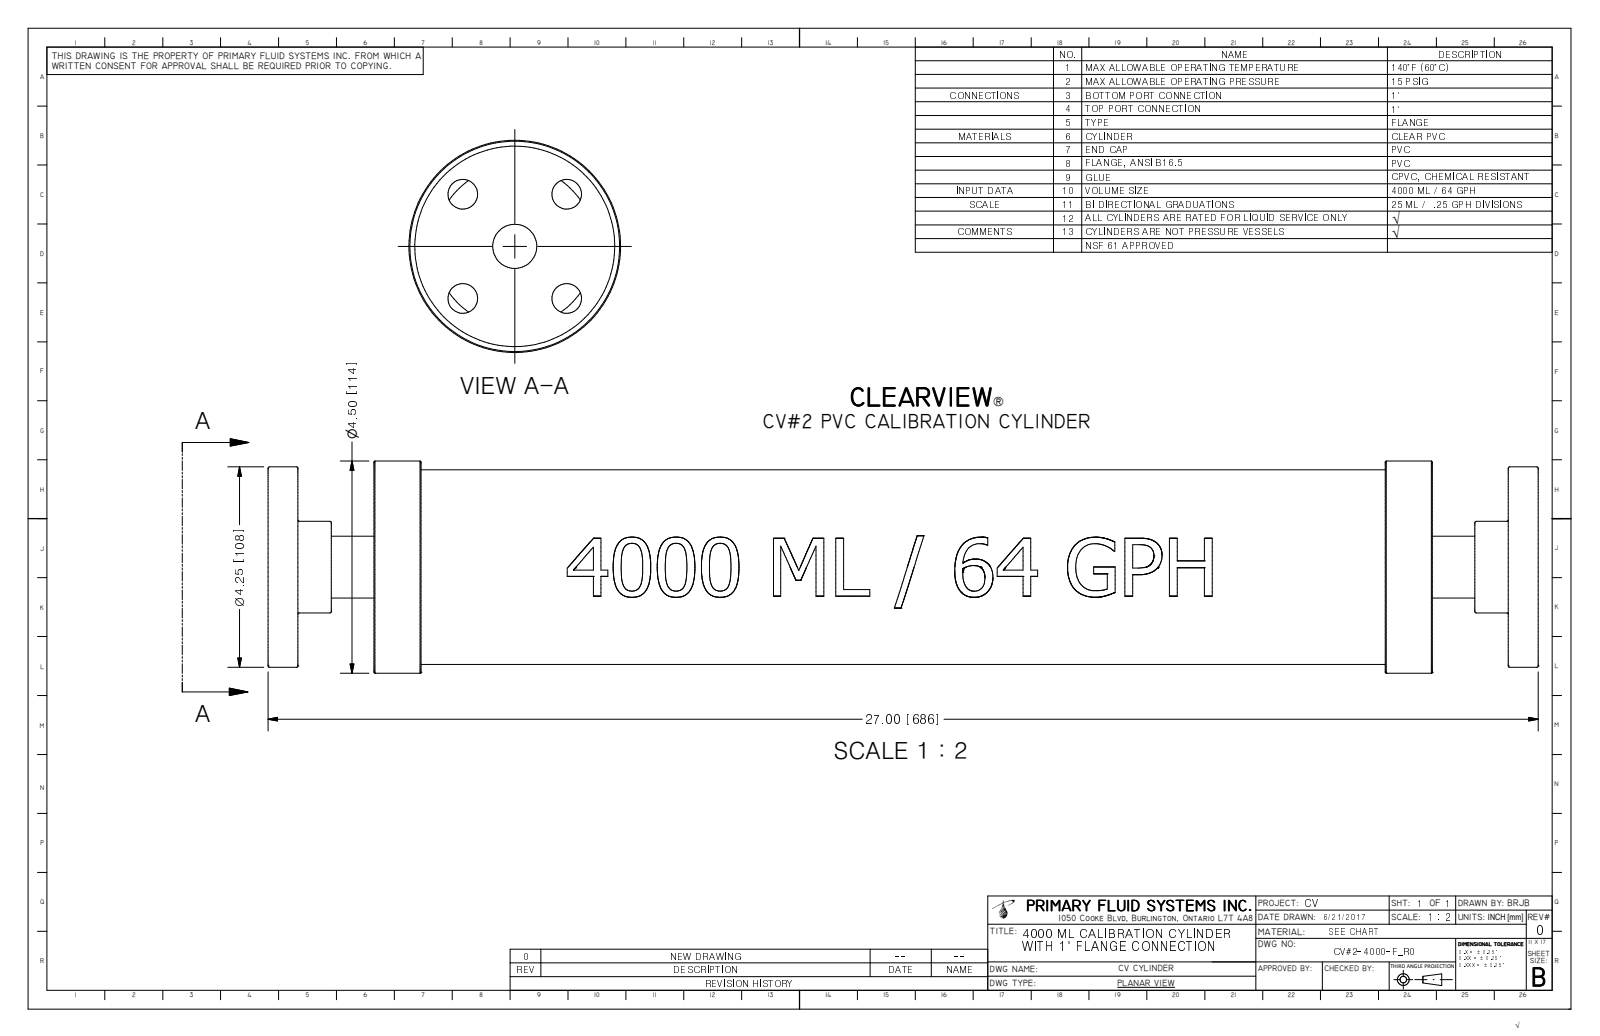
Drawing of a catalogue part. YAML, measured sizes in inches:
part_name: "PV#2-4000-F_R0"
step_written_by: "Autodesk Inventor 2009 (AUTOMOTIVE_DESIGN)"
units: inches
bodies: {solids: 1, faces: 356, planar: 118, cylindrical: 47, other: 191}
overall_size: [27, 4.5, 4.5]
volume: 58.19
surface_area: 809.4
round_holes:
  - {diameter: 0.63, count: 4}
  - {diameter: 0.936, count: 1}
  - {diameter: 0.957, count: 1}
  - {diameter: 1.156, count: 1}
  - {diameter: 4.005, count: 1}
  - {diameter: 4.15, count: 1}
round_bosses_or_shafts:
  - {diameter: 4.5, count: 1}
  - {diameter: 4.25, count: 1}
  - {diameter: 4.125, count: 1}
  - {diameter: 3.876, count: 1}
  - {diameter: 1.941, count: 1}
  - {diameter: 1.315, count: 1}
partial_cylinders:
  - {radius: 2.061, count: 1}
face_to_face_distances: [0.635, 26.365, 2.25, 24.75, 1.615, 24.115, 27, 0.5, 25.73, 21.5]
hole_center_spacings: [1.562, 2.209, 3.125]
